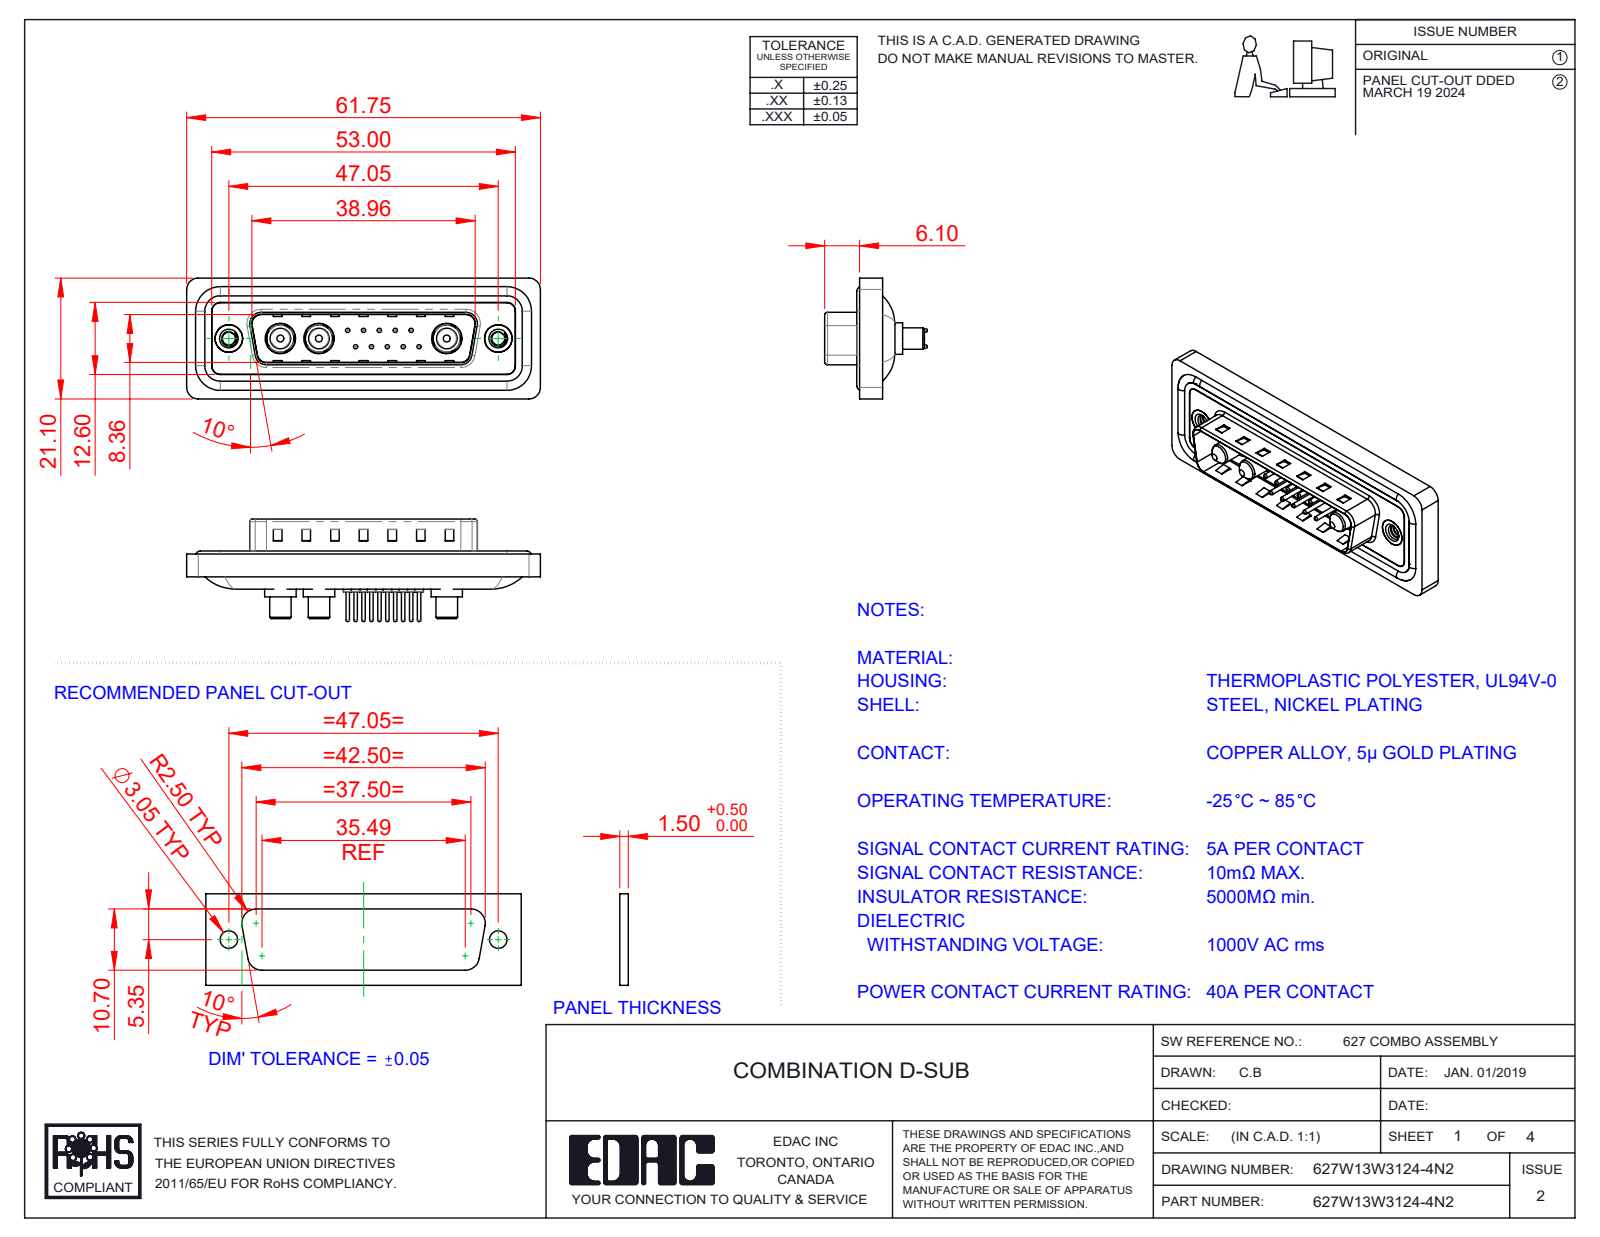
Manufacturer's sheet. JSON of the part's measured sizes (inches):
{"part_name": "627W13W3124-4N2; 627Combo Contact Row 1_24; Power Pin_40A S; 627Combo Shell Front_25 Contacts (+5 more)", "step_written_by": "SolidWorks 2023 (CONFIG_CONTROL_DESIGN)", "units": "inches", "bodies": {"solids": 23, "faces": 970, "planar": 309, "cylindrical": 385, "other": 276}, "overall_size": [2.431, 0.831, 0.705], "volume_in3": 0.451, "surface_area_in2": 18.46, "round_holes": [[0.03, 10], [0.063, 10], [0.079, 10], [0.191, 3], [0.209, 3], [0.089, 2], [0.157, 2], [0.189, 2], [0.197, 2]], "round_bosses_or_shafts": [[0.059, 10], [0.024, 10], [0.063, 4], [0.217, 3], [0.205, 3], [0.187, 3], [0.148, 3], [0.142, 3]], "partial_cylinders_radius": [[0.059, 22], [0.079, 18], [0.02, 8], [0.063, 8], [0.01, 4], [0.024, 4], [0.026, 4], [0.035, 4]], "face_to_face_distances": [0.016, 0.059, 0.043, 0.063, 0.02, 0.122, 0.114, 0.032, 0.377, 0.161], "hole_center_spacings": [0.124, 0.109, 0.198, 0.218, 0.295, 0.198, 0.327, 0.398]}
